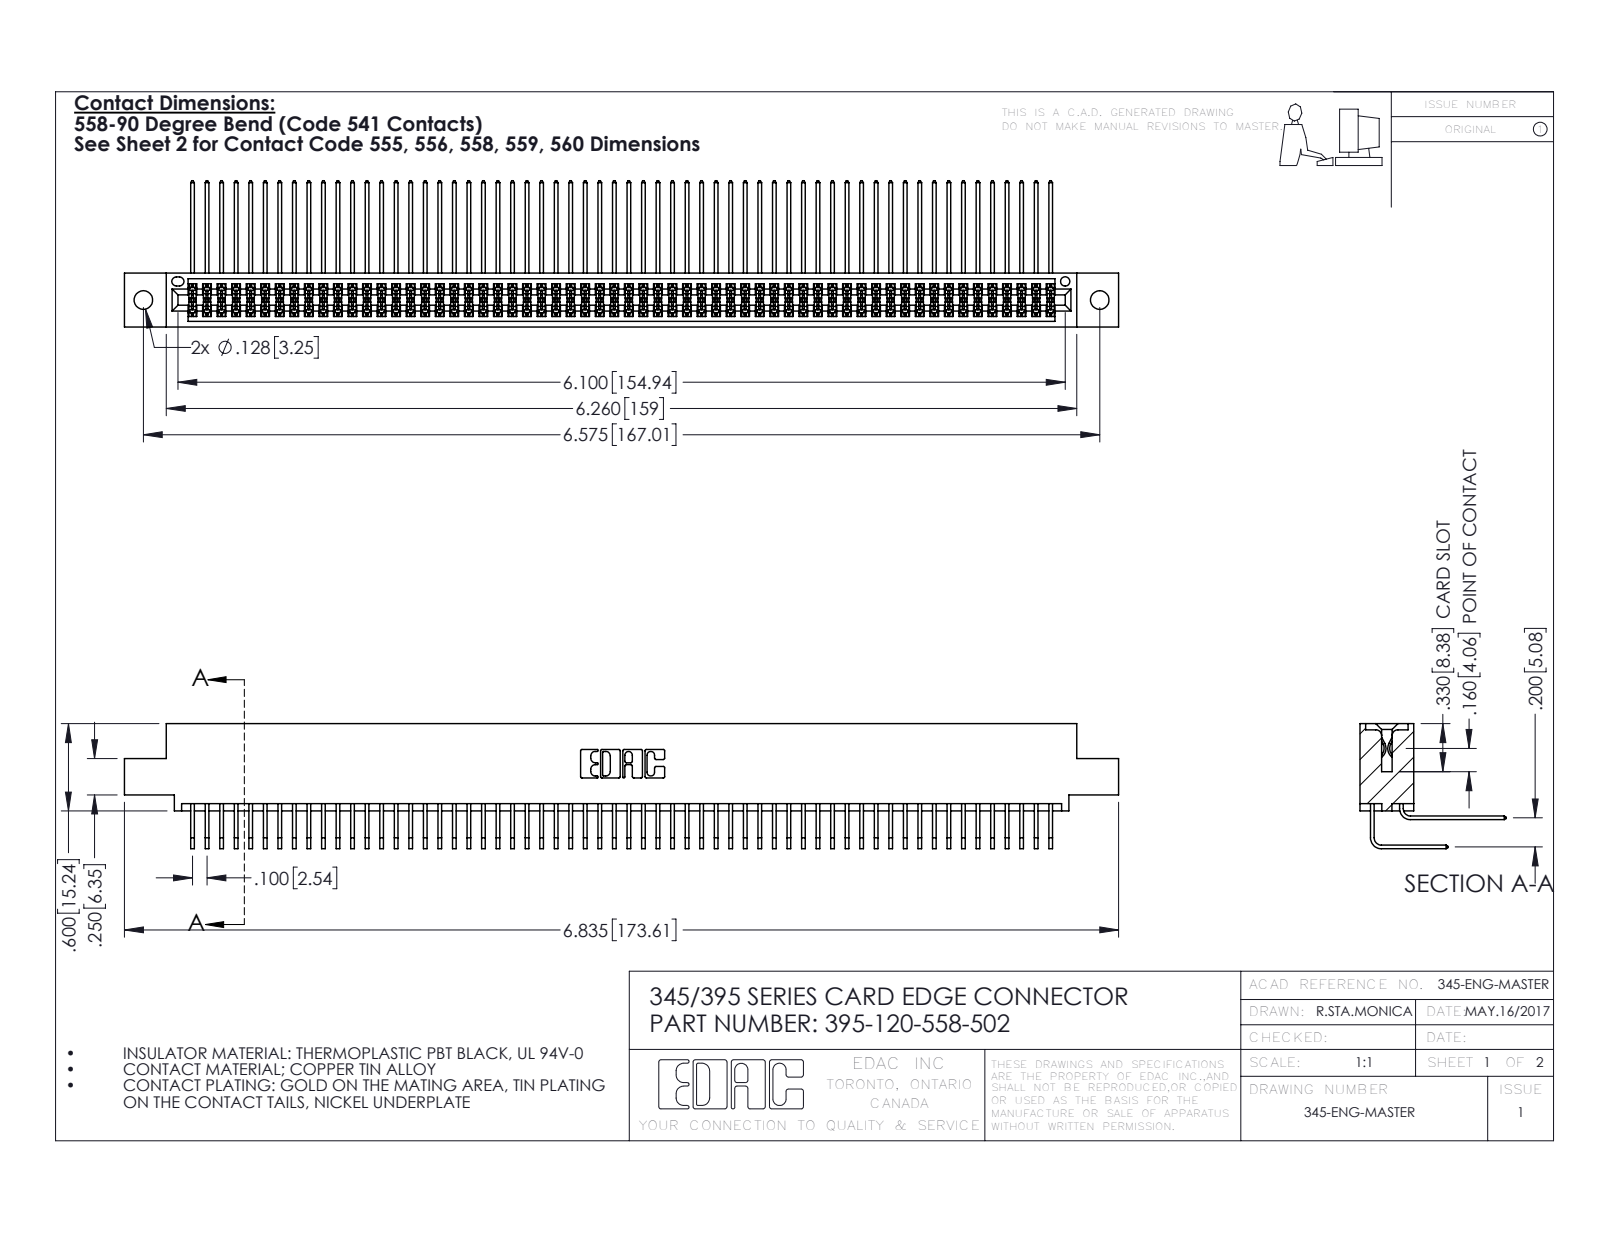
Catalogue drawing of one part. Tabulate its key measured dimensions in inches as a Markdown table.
| quantity | value |
| --- | --- |
| part name | 345-292-001_558 Tail - 2; 345 Part_0.110 Offset - 0.128 Dia; 395-120-558-502; 345-292-001_558 559 Tail - 1 |
| STEP written by | SolidWorks 2016 (CONFIG_CONTROL_DESIGN) |
| units | inches |
| bodies | 121 solids, 6370 faces (4284 planar, 2086 cylindrical, 0 other) |
| overall size | 6.835 × 1.005 × 0.859 |
| volume | 1.075 in³ |
| surface area | 45.66 in² |
| round holes (diameter × count) | 0.128 × 2, 0.064 × 1 |
| partial cylindrical surfaces (radius × count) | 0.006 × 181, 0.01 × 22, 0.007 × 6, 0.031 × 6, 0.026 × 3, 0.014 × 2, 0.019 × 2, 0.022 × 2 |
| main face-to-face distances | 0.072, 0.298, 0.2, 0.37, 0.098, 0.272, 0.025, 0.225, 0.025, 0.175 |
| hole center spacings | 0.27, 6.339, 6.575 |
